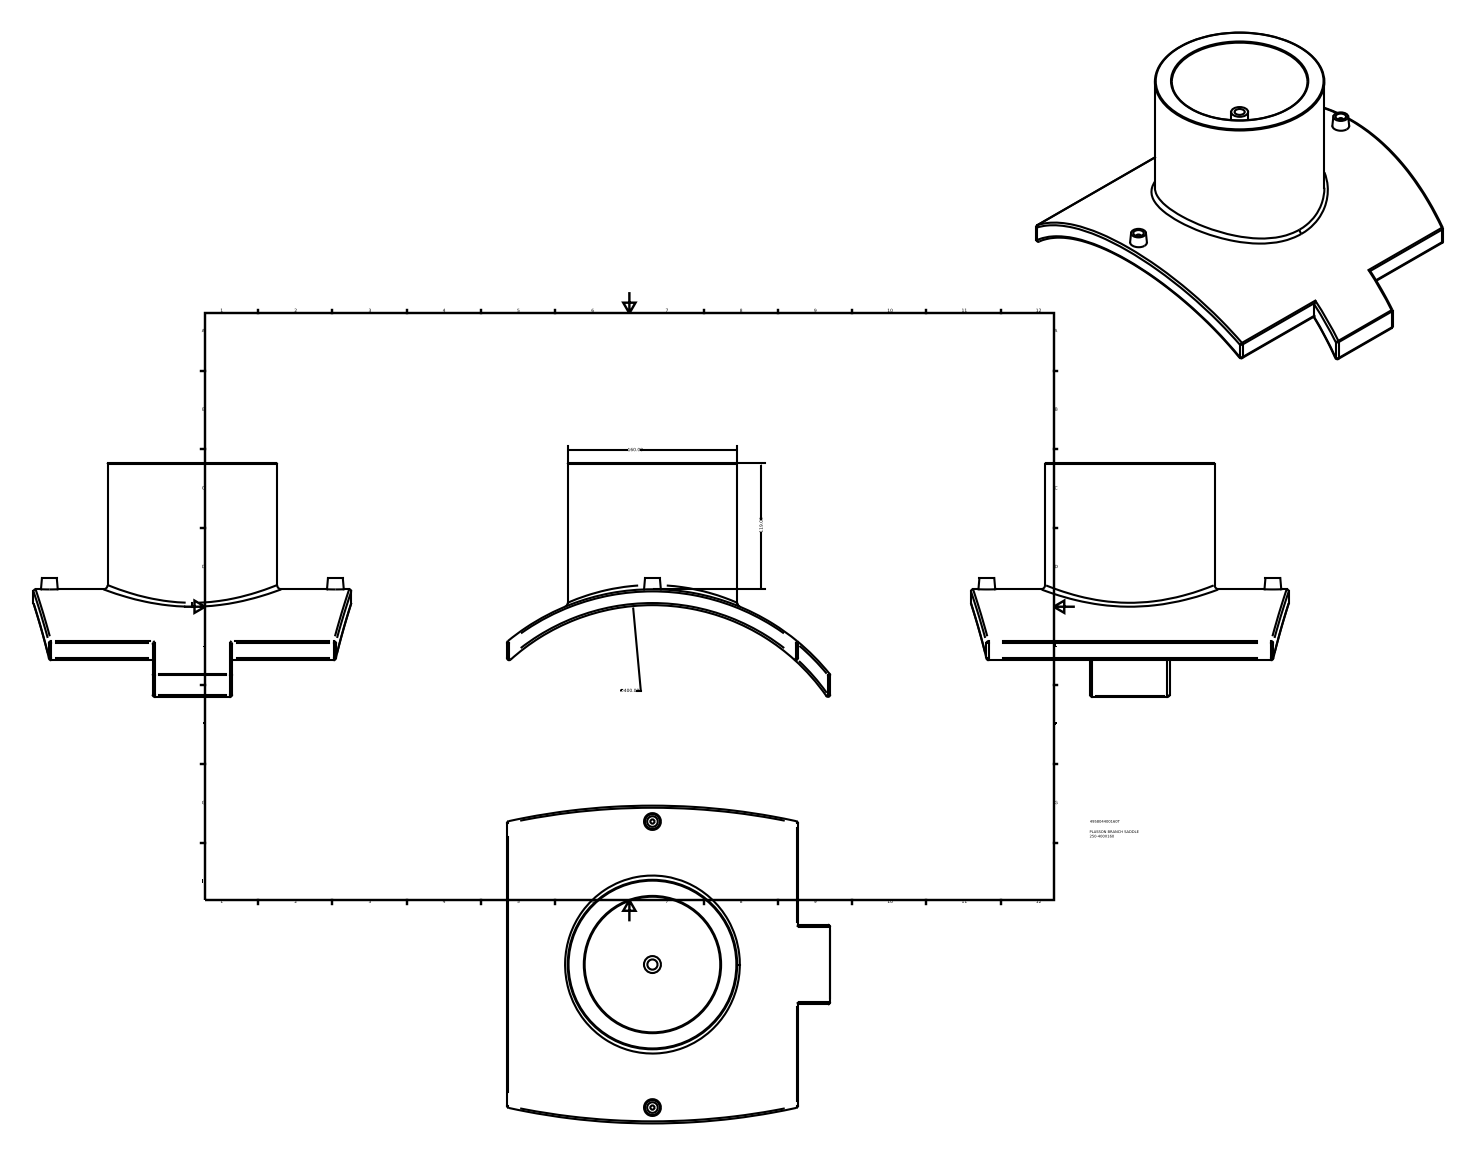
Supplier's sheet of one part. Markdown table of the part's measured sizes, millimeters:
| quantity | value |
| --- | --- |
| part name | 495804400160T |
| STEP written by | Autodesk Inventor 2015 (AUTOMOTIVE_DESIGN) |
| units | millimeters |
| bodies | 1 solid, 66 faces (14 planar, 27 cylindrical, 25 other) |
| overall size | 305 × 300 × 220.54 |
| volume | 2 268 000 mm³ |
| surface area | 319 538 mm² |
| round holes (diameter × count) | 10 × 2, 9.6 × 1, 128 × 1 |
| round bosses / shafts (diameter × count) | 4 × 2, 160 × 1, 16 × 1 |
| partial cylindrical surfaces (radius × count) | 2 × 12, 635.42 × 2, 200 × 1, 215 × 1 |
| main face-to-face distances | 274.5, 305, 30.5, 75, 108.4, 14, 122.4, 86.7, 72.7, 35.7 |
| hole center spacings | 135, 270 |
